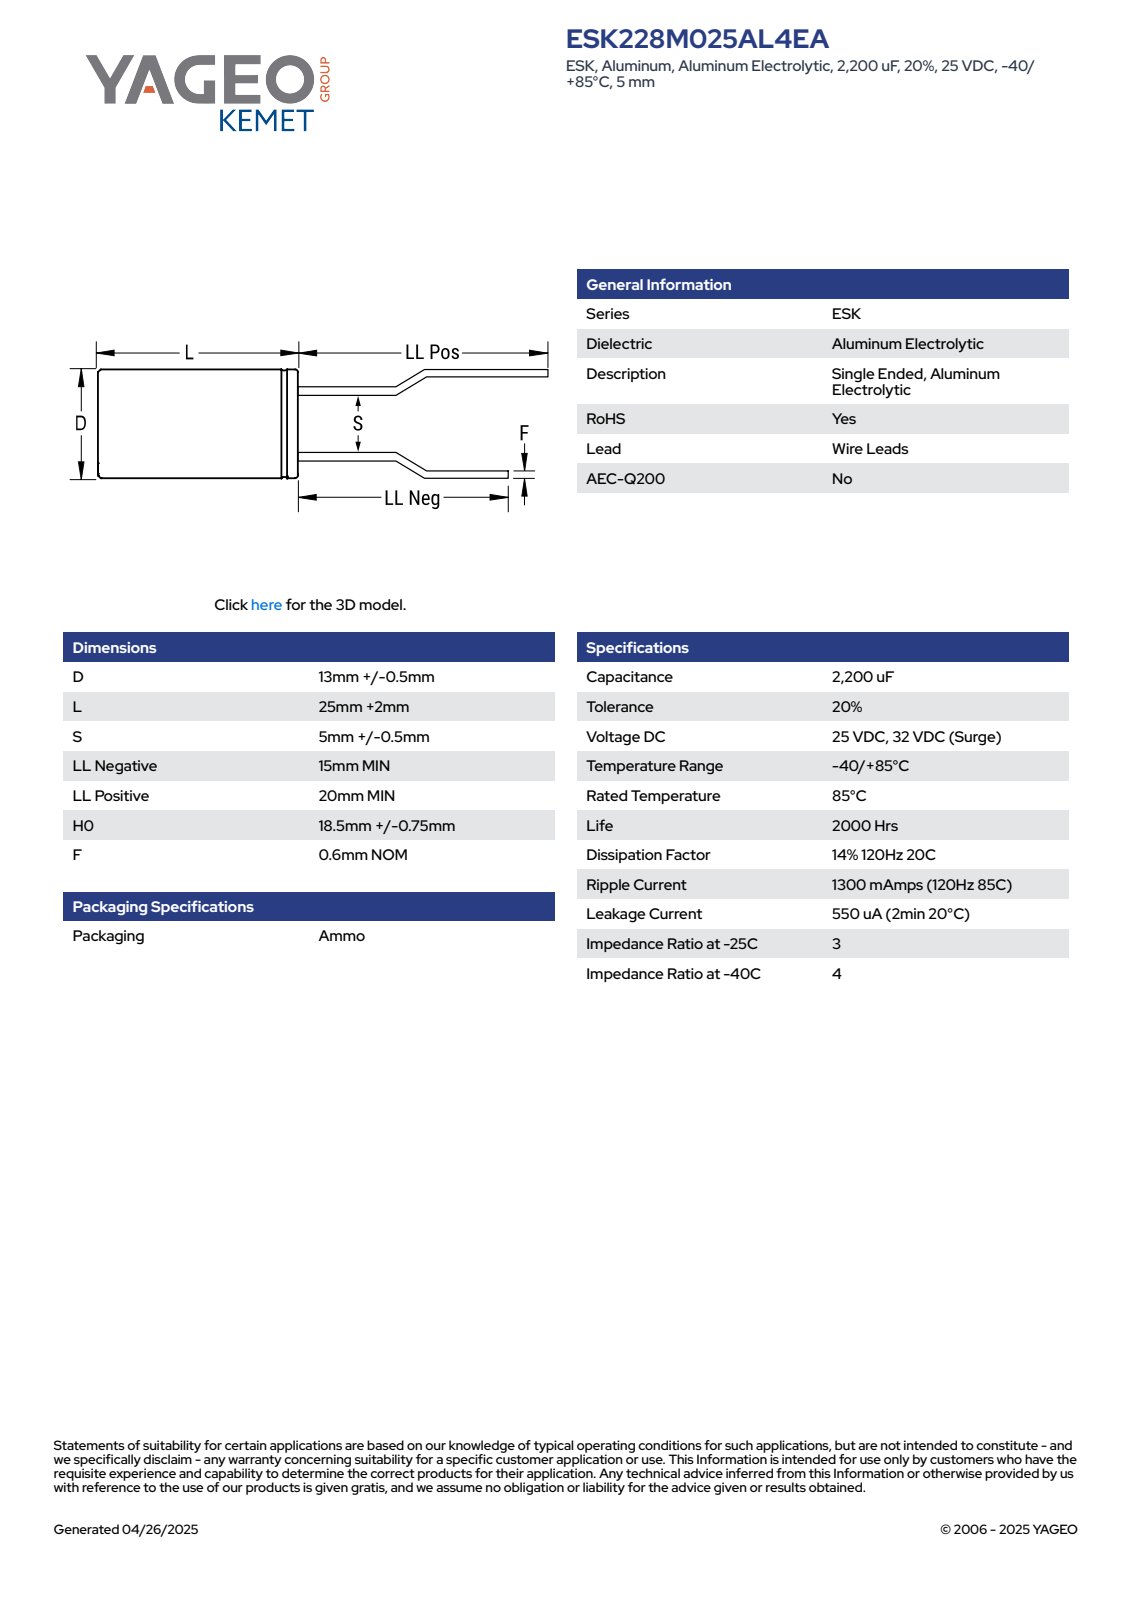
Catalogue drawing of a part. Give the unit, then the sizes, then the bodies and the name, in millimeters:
Units: millimetres
Overall size (bounding box): 47.01 × 13.5 × 13.5
Round bosses / shafts (diameter × count): ⌀0.6 ×2, ⌀13.5 ×1
Main face-to-face distances: 27, 27.01, 42.01, 47.01, 42, 47, 15, 20, 5, 1.6
Volume: 3 849 mm³ · Surface area: 1 538 mm²
Bodies: 4 solids, 73 faces (61 planar, 8 cylindrical, 4 other)
Part name (STEP PRODUCT): CAR_KTRS_13X25_D13.5L27S5F0.6
STEP written by: SolidWorks 2014 (AUTOMOTIVE_DESIGN)
